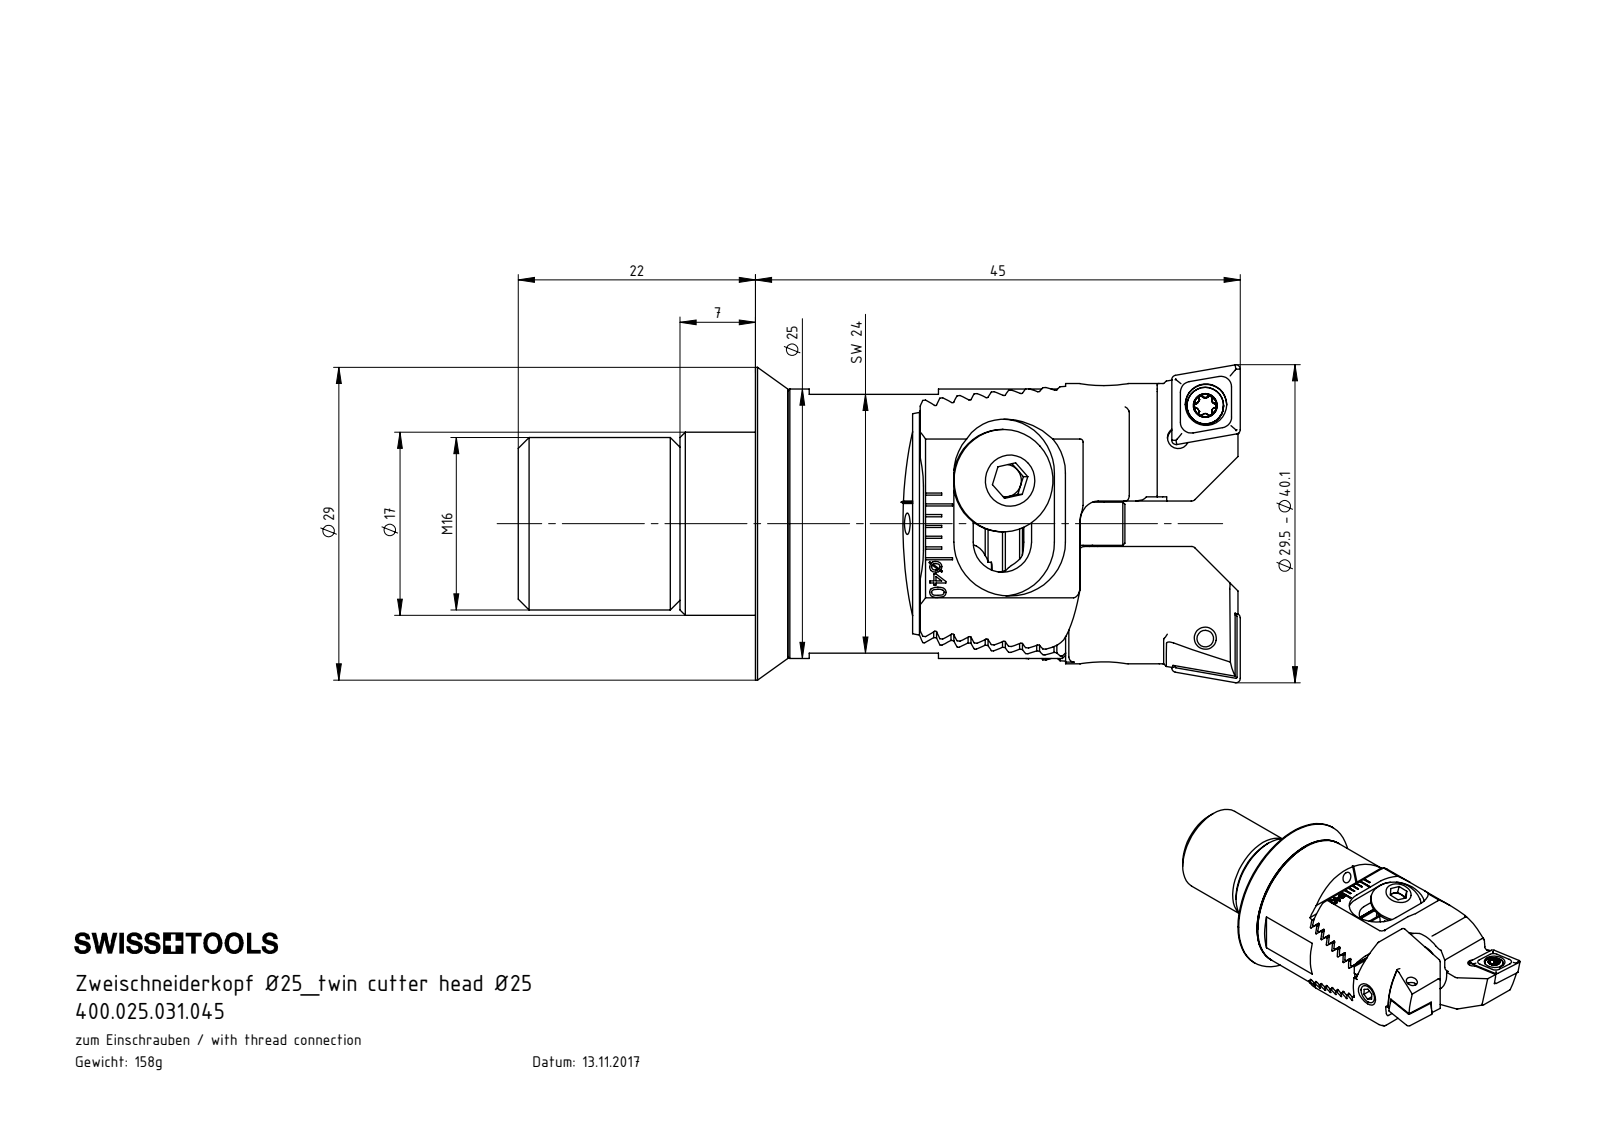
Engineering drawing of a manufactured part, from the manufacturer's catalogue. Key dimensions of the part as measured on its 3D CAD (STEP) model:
Part name (STEP PRODUCT): Z25-ER1.003.012_A_gespannt; Z25-ER1.001.012; HP5-Z25.030.045_A; Z25-ER3.001.010_A (+8 more)
STEP written by: SolidWorks 2017 (CONFIG_CONTROL_DESIGN)
Units: millimetres
Bodies: 16 solids, 1016 faces (502 planar, 250 cylindrical, 264 other)
Overall size (bounding box): 67 × 29.5 × 28
Volume: 19 637 mm³ · Surface area: 13 724 mm²
Round holes (diameter × count): ⌀2 ×5, ⌀1.6 ×2, ⌀2.05 ×2, ⌀2.8 ×2, ⌀3.85 ×2, ⌀4.2 ×2, ⌀6 ×2, ⌀2.5 ×1, ⌀3.3 ×1, ⌀3.5 ×1, ⌀5.3 ×1, ⌀10.6 ×1
Round bosses / shafts (diameter × count): ⌀9.5 ×2, ⌀5 ×2, ⌀4 ×2, ⌀3.4 ×2, ⌀2.5 ×2, ⌀28 ×1, ⌀25 ×1, ⌀16 ×1
Partial cylindrical surfaces — rounded edges, fillets, slot ends (radius × count): R0.12 ×18, R0.5 ×18, R0.12 ×16, R0.21 ×12, R0.36 ×10, R2 ×4, R2.8 ×4, R5 ×4
Main face-to-face distances: 1.43, 2.86, 7.14, 5.71, 3, 1.39, 1.47, 8.57, 4.28, 10
Hole centre spacings: 3.91, 4.01, 7, 19.06, 19.15, 21.97, 13.52, 15.9
